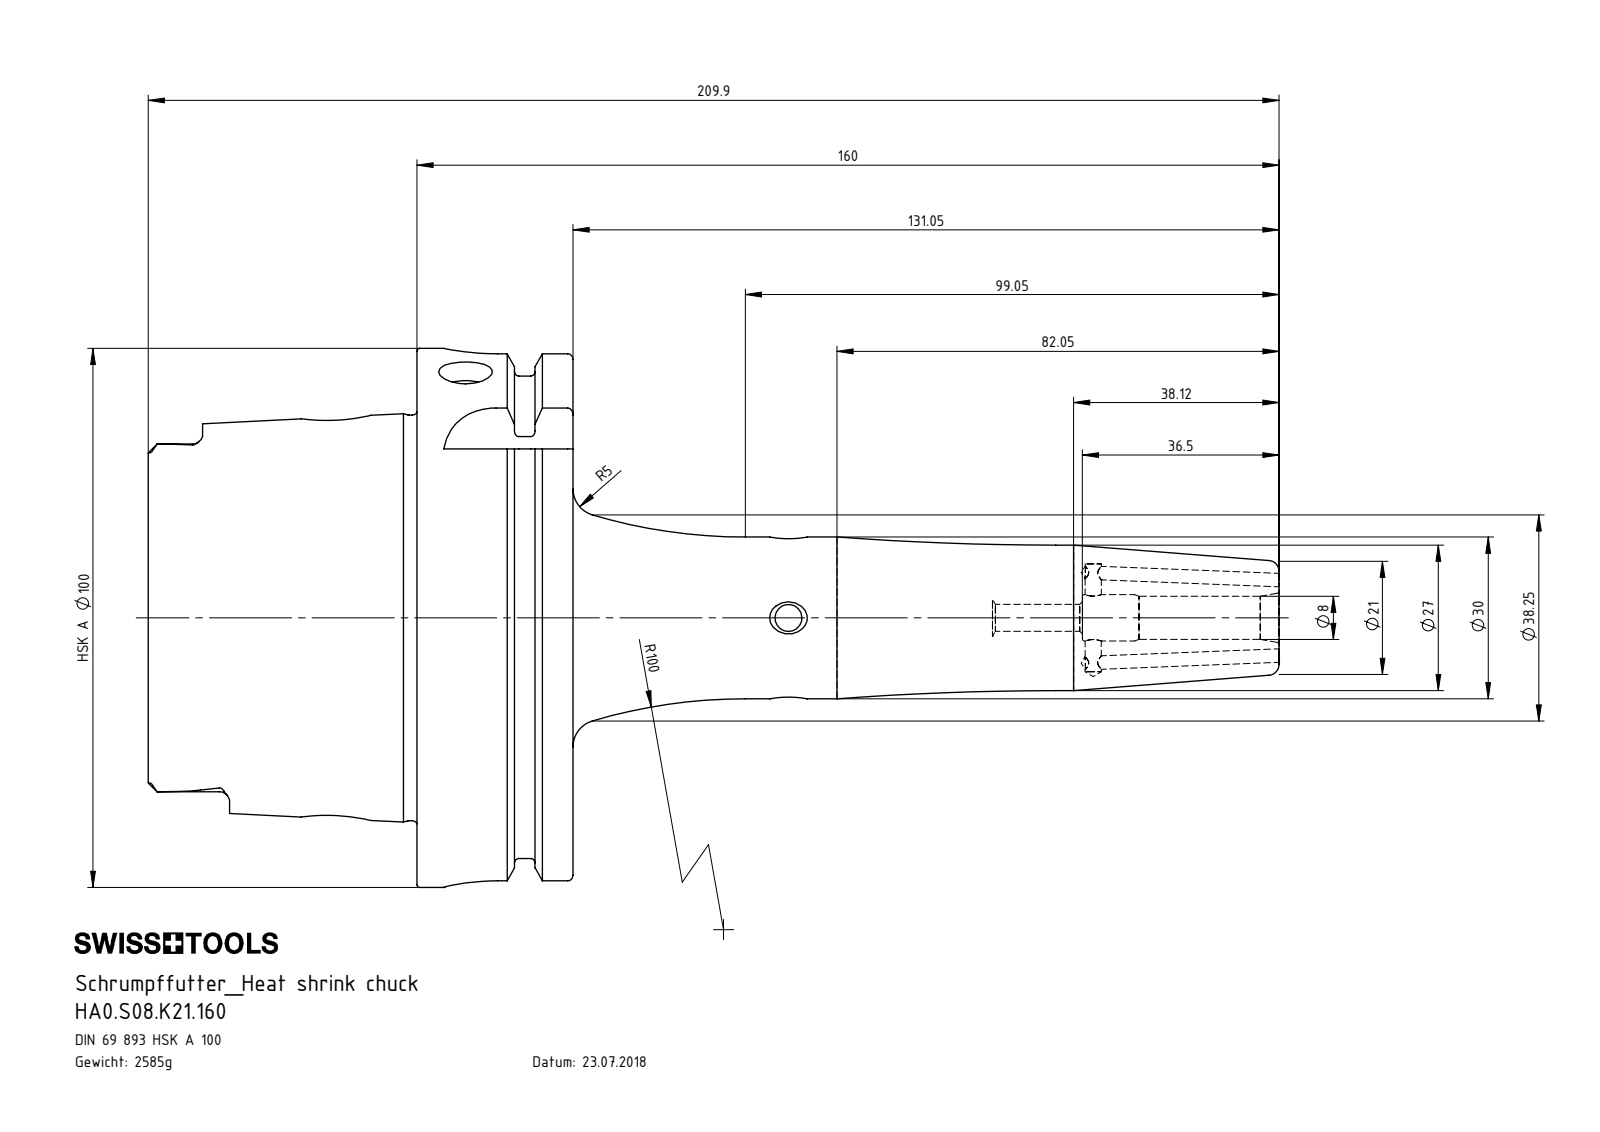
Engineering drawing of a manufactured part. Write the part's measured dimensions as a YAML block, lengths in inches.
part_name: "HA0.S08.K21.160; ERU-CJ2.001.006; ERU-AN2.K01.016_A; HA0-S08.K21.160_C_Fertigbearbeitung"
step_written_by: "SolidWorks 2017 (CONFIG_CONTROL_DESIGN)"
units: inches
bodies: {solids: 4, faces: 309, planar: 95, cylindrical: 90, other: 124}
overall_size: [8.267, 3.937, 3.937]
volume: 20.09
surface_area: 101.8
round_holes:
  - {diameter: 0.197, count: 3}
  - {diameter: 0.394, count: 3}
  - {diameter: 0.098, count: 2}
  - {diameter: 0.118, count: 2}
  - {diameter: 0.472, count: 2}
  - {diameter: 0.268, count: 1}
  - {diameter: 0.315, count: 1}
  - {diameter: 0.339, count: 1}
  - {diameter: 0.886, count: 1}
  - {diameter: 1.024, count: 1}
  - {diameter: 2.087, count: 1}
  - {diameter: 2.48, count: 1}
round_bosses_or_shafts:
  - {diameter: 0.118, count: 2}
  - {diameter: 3.937, count: 1}
  - {diameter: 3.62, count: 1}
  - {diameter: 2.963, count: 1}
  - {diameter: 1.181, count: 1}
  - {diameter: 1.063, count: 1}
  - {diameter: 0.236, count: 1}
partial_cylinders:
  - {radius: 0.075, count: 6}
  - {radius: 0.192, count: 4}
  - {radius: 0.394, count: 4}
face_to_face_distances: [1.14, 0.49, 0.65, 1.965, 2.455, 3.104, 3.457, 3.079, 1.114, 0.624]
hole_center_spacings: [2.226, 2.439, 3.305, 5.531]
